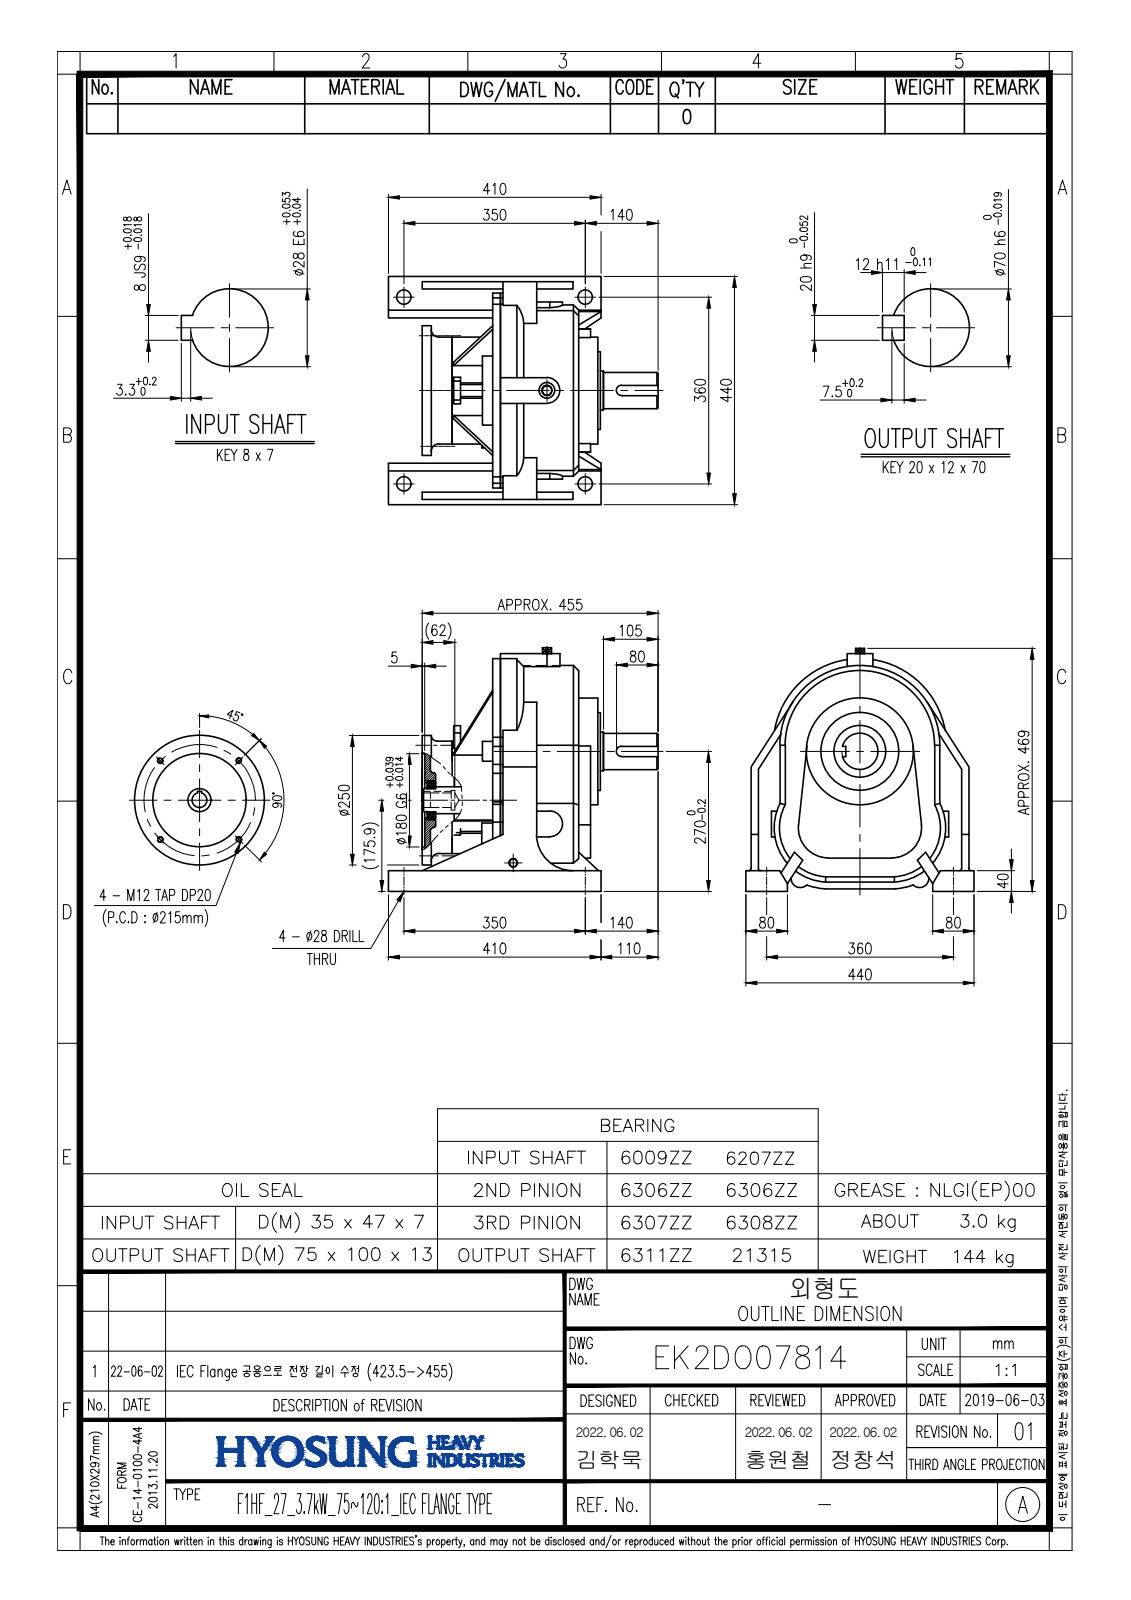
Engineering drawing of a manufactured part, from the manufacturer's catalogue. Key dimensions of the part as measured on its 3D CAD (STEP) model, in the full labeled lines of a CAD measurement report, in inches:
Part name (STEP PRODUCT): DKA0800233_BRACKET; CASING_DKA0102313; EK2DO07814H001_F1HF_3.7KW_R75; 27_3.7KW (+1 more)
STEP written by: SolidWorks 2021 (AUTOMOTIVE_DESIGN)
Units: inches
Bodies: 4 solids, 530 faces (123 planar, 225 cylindrical, 182 other)
Overall size (bounding box): 20.472 × 18.071 × 17.323
Volume: 1 934 in³ · Surface area: 2 102 in²
Round holes (diameter × count): ⌀0.709 ×10, ⌀0.551 ×9, ⌀0.402 ×7, ⌀1.102 ×4, ⌀0.268 ×3, ⌀0.354 ×3, ⌀0.106 ×2, ⌀0.512 ×2, ⌀2.598 ×1, ⌀7.087 ×1
Round bosses / shafts (diameter × count): ⌀8.11 ×2, ⌀9.843 ×1, ⌀5.906 ×1, ⌀2.953 ×1, ⌀2.756 ×1
Partial cylindrical surfaces — rounded edges, fillets, slot ends (radius × count): R0.197 ×37, R0.118 ×32, R0.394 ×11, R0.709 ×8, R0.039 ×5, R0.079 ×4, R0.787 ×4, R0.512 ×3
Main face-to-face distances: 0.591, 3.071, 3.661, 5.945, 1.575, 0.551, 7.402, 0.197, 0.394, 1.654
Hole centre spacings: 7.228, 1.099, 3.258, 4.232, 6.669, 7.82, 8.119, 10.362
